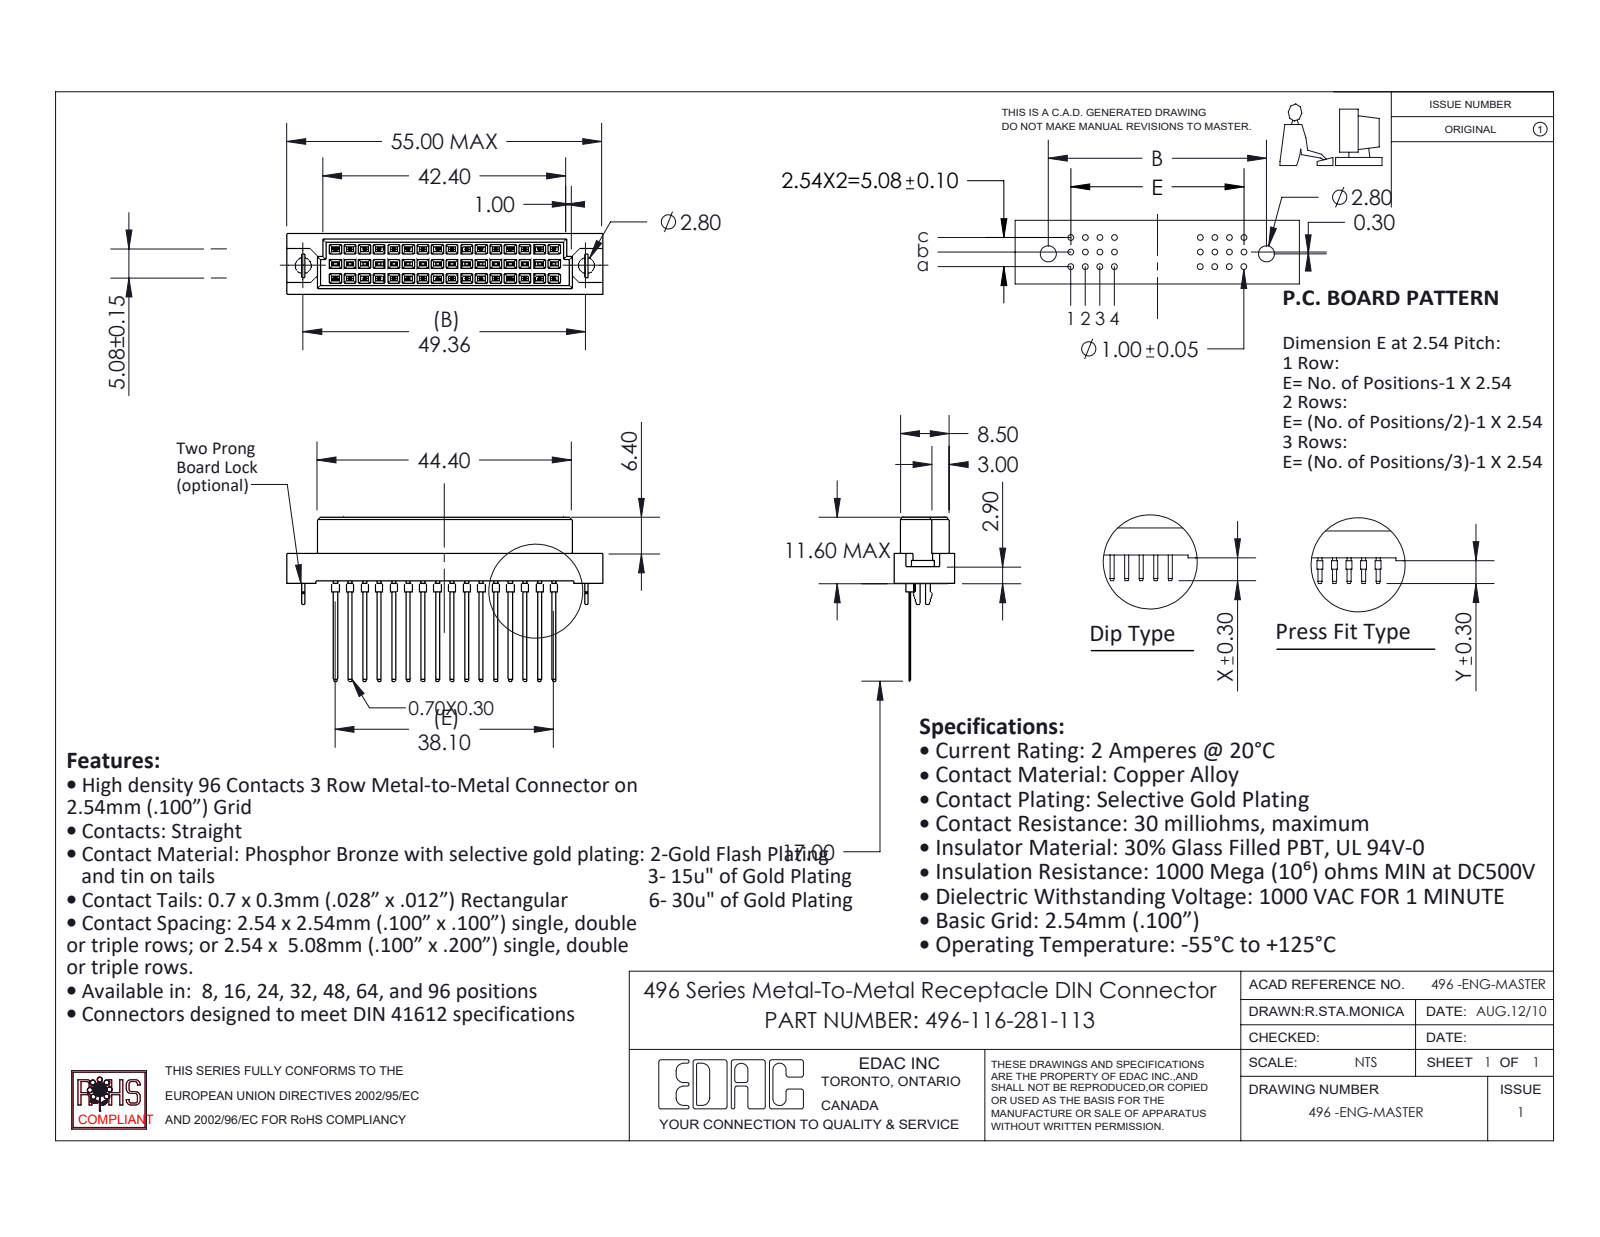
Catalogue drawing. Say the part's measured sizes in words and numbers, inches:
The part is named "496 Bore-lock; 496 Part_48; 496-290_81; 496-116-281-113". Its 3-D file was written by "SolidWorks 2020 (CONFIG_CONTROL_DESIGN)". It is 19 solids with 990 faces: 952 planar, 38 cylindrical and 0 other. Overall it measures 2.165 by 1.126 by 0.417 inches. Its volume is 0.287 cubic inches and its surface area 7.848 square inches. Round holes: 2 of diameter 0.11. Round bosses or shafts: 16 of diameter 0.039. Partial cylindrical surfaces (rounded edges, fillets, slot ends): 1 of radius 0.021. The main face-to-face distances are 0.1, 0.041, 0.376, 0.2, 0.032, 0.073, 0.061, 0.115, 0.303, 0.103. The hole center spacings are 1.943.
